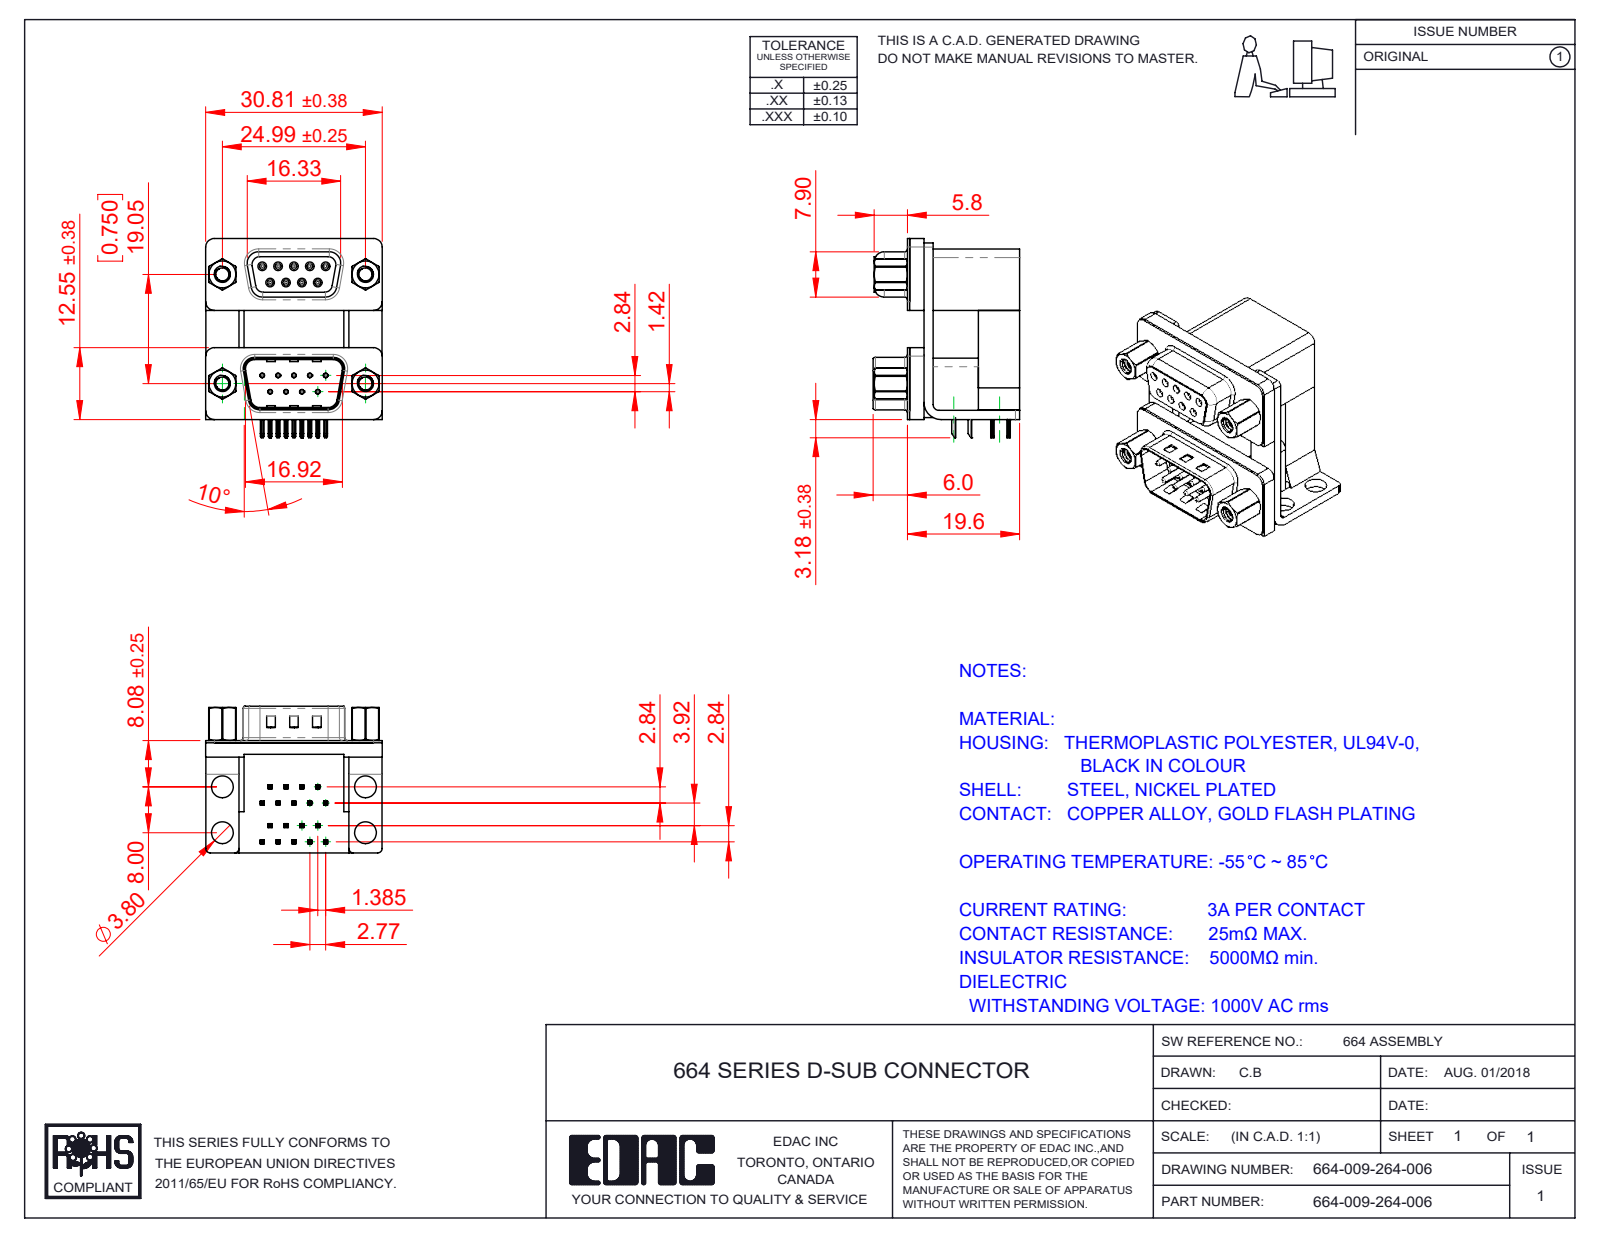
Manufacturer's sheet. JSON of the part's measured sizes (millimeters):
{"part_name": "664 Housing Lower_09 Contacts; 664 Contact Top Upper_M; 664 Contact Bottom Lower; 664 Shell Plug_09 Contacts (+8 more)", "step_written_by": "SolidWorks 2020 (CONFIG_CONTROL_DESIGN)", "units": "millimeters", "bodies": {"solids": 33, "faces": 2781, "planar": 1307, "cylindrical": 839, "other": 635}, "overall_size": [34.78, 30.81, 25.6], "volume_mm3": 11179, "surface_area_mm2": 13470, "round_holes": [[0.8, 18], [0.35, 9], [0.9, 9], [2.26, 4], [2.29, 4], [3.5, 4], [3.8, 4], [4, 4], [4.8, 4], [5, 4]], "round_bosses_or_shafts": [[1.2, 9], [0.75, 9], [4.9, 4], [4.75, 4], [3.9, 4], [2.79, 4]], "partial_cylinders_radius": [[0.1, 72], [0.15, 36], [0.25, 36], [0.12, 18], [0.35, 18], [1.5, 13], [0.5, 12], [0.34, 9]], "face_to_face_distances": [0.4, 2.5, 16.7, 19.2, 7.2, 9.5, 12, 19.6, 12.4, 2.9], "hole_center_spacings": [3.16, 2.77, 19.25, 19.05, 5.54, 19.84, 16.27, 21.93]}
